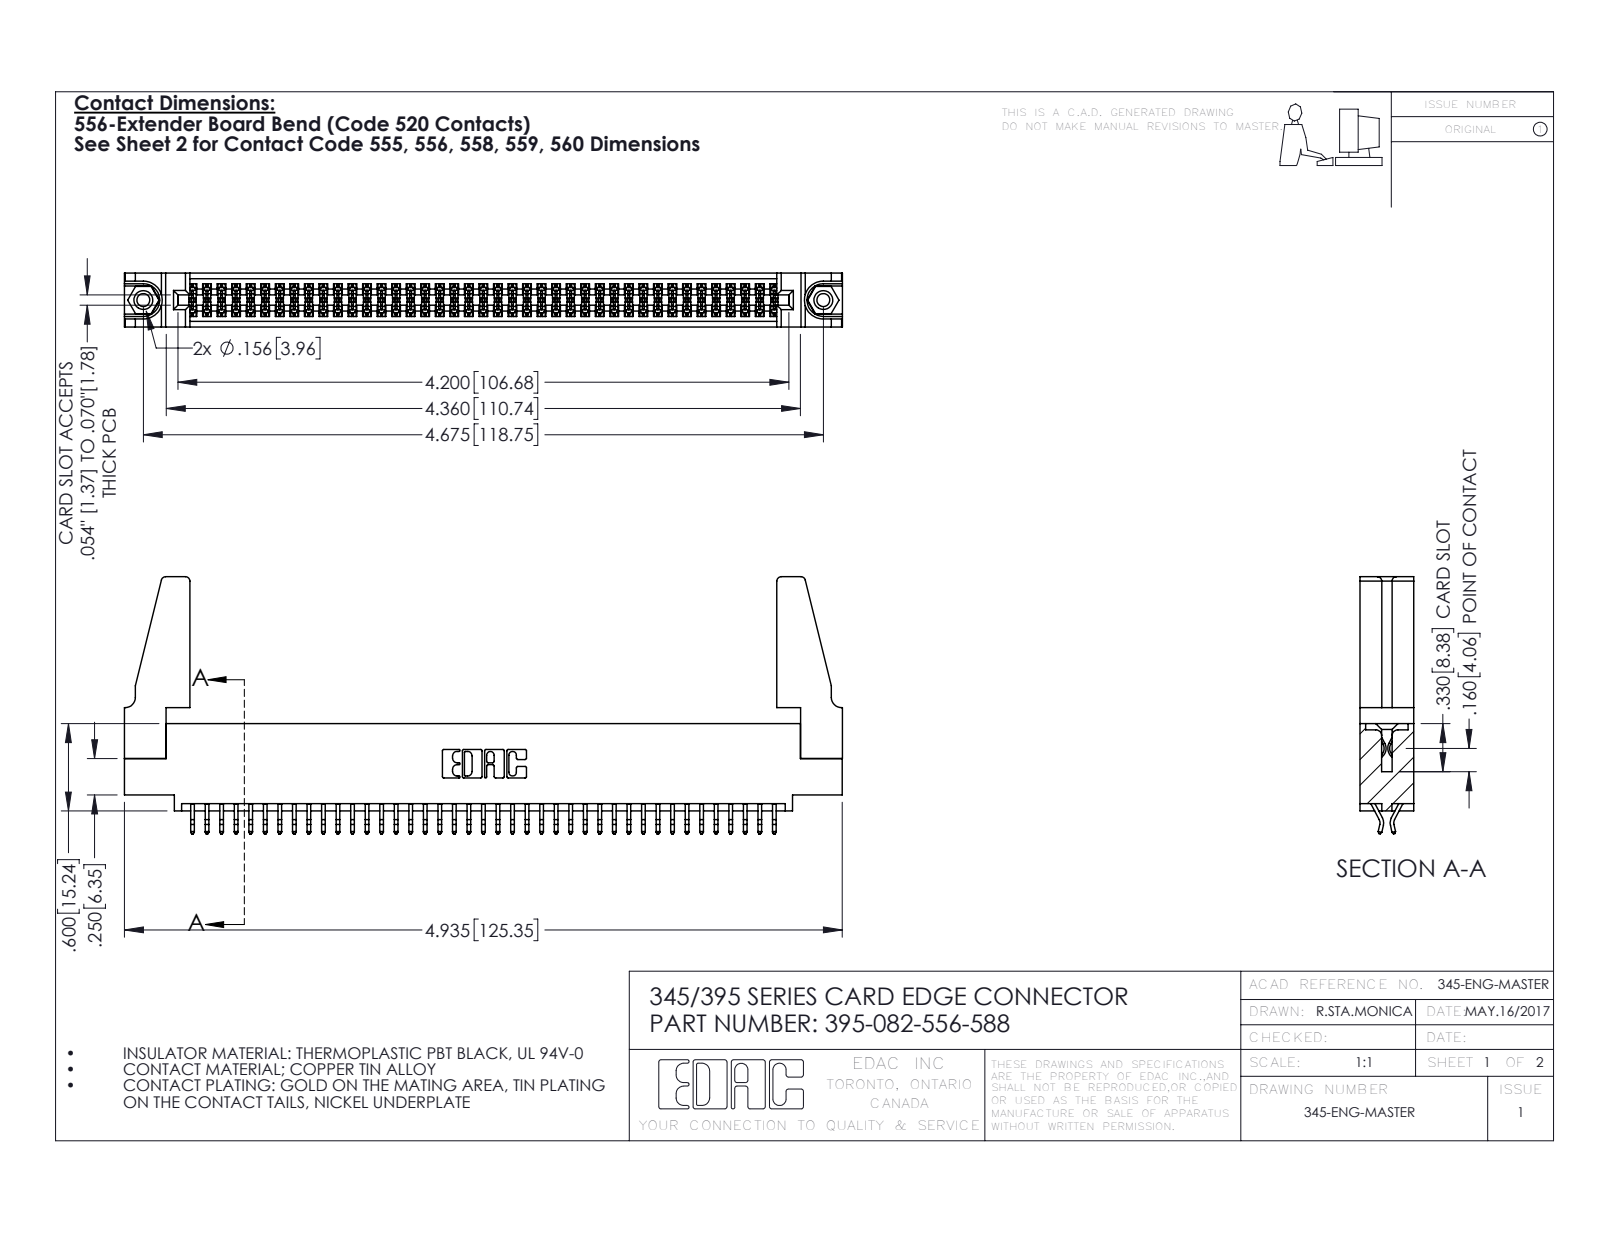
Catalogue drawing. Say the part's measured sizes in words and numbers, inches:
The part is named "345-250-001_345-250-001-102; 345 Part_0.110 Offset - 0.156 Dia-TH; 345-220-078_345-220-088; 345-292-001_556 Tail (+1 more)". Its 3-D file was written by "SolidWorks 2016 (CONFIG_CONTROL_DESIGN)". It is 87 solids with 4846 faces: 3190 planar, 1640 cylindrical and 16 other. Overall it measures 4.936 by 1.767 by 0.37 inches. Its volume is 0.936 cubic inches and its surface area 32.55 square inches. Round holes: 2 of diameter 0.089, 2 of diameter 0.125, 2 of diameter 0.156, 1 of diameter 0.064. Round bosses or shafts: 2 of diameter 0.155. Partial cylindrical surfaces (rounded edges, fillets, slot ends): 123 of radius 0.006, 22 of radius 0.01, 8 of radius 0.03, 6 of radius 0.007, 6 of radius 0.031, 3 of radius 0.026, 2 of radius 0.01, 2 of radius 0.014. The main face-to-face distances are 0.072, 0.298, 0.37, 0.025, 0.2, 0.098, 0.272, 0.225, 0.175, 0.149. The hole center spacings are 0.27, 4.439, 4.675.
